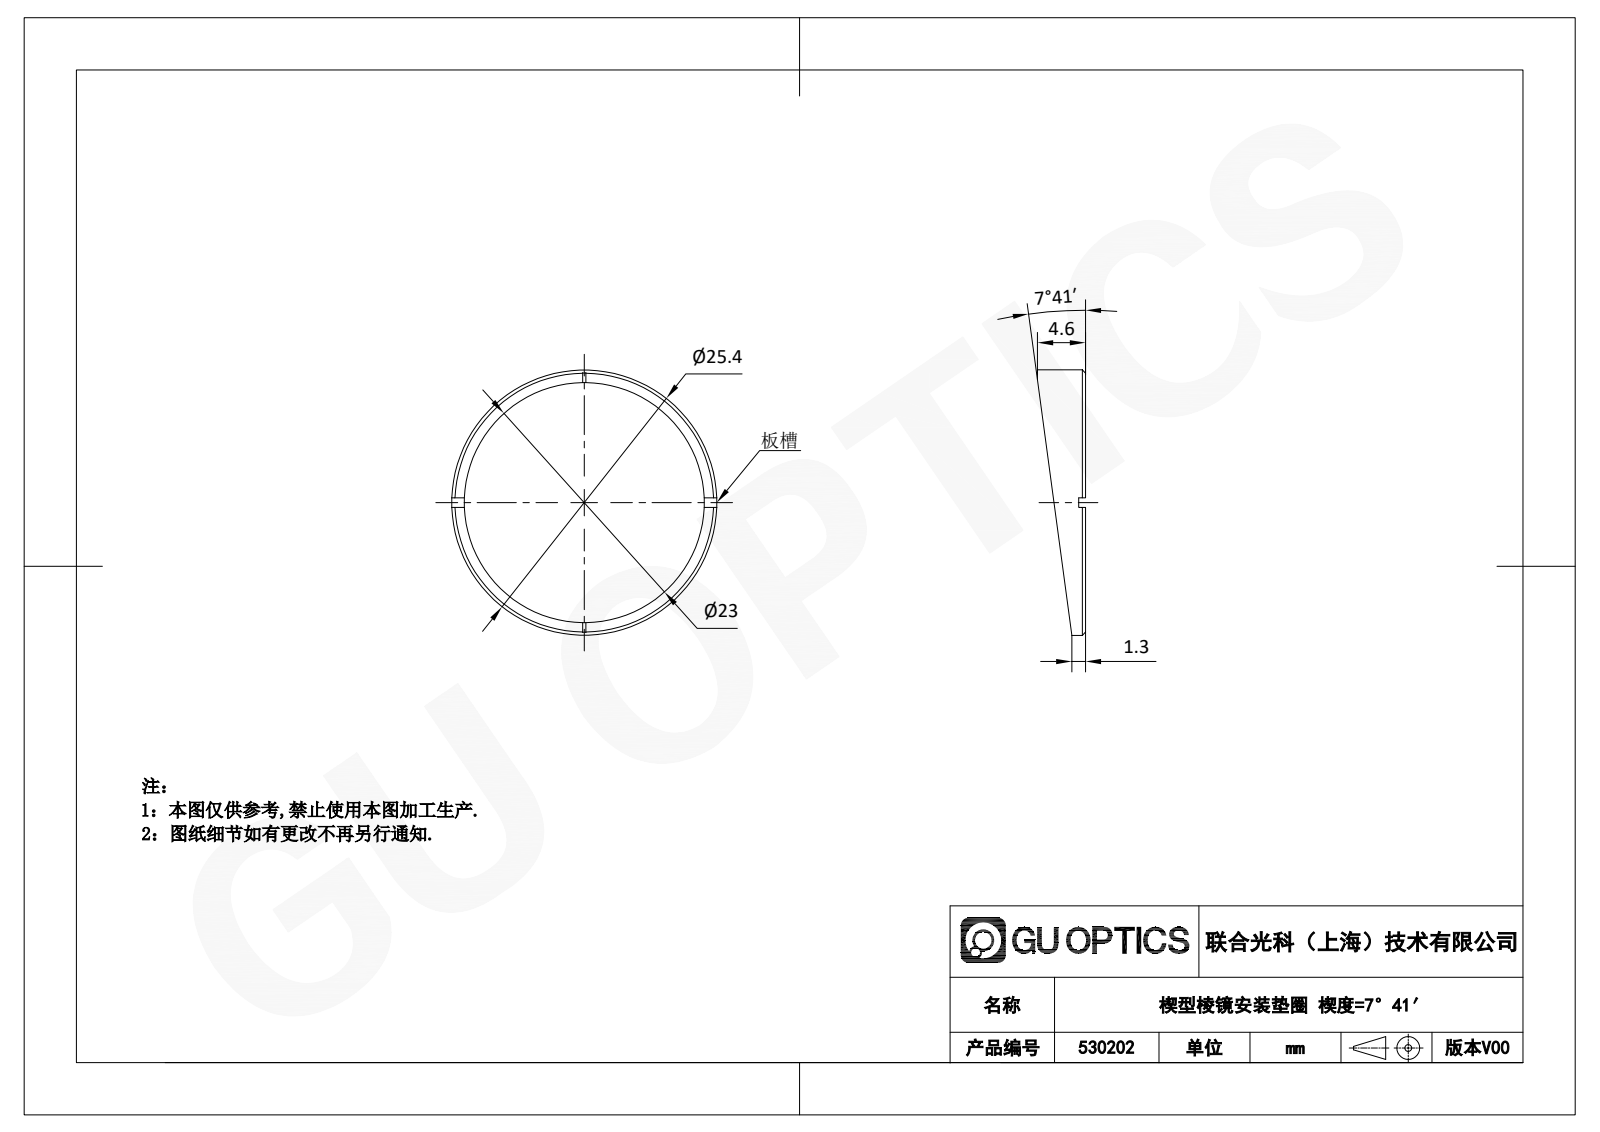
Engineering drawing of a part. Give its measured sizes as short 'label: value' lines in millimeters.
name: 530202
written by: SolidWorks 2020 (CONFIG_CONTROL_DESIGN)
unit: mm
bodies: 1 solid, 22 faces (18 planar, 2 cylindrical, 2 other)
size: 25.4 × 25.4 × 4.6
volume: 265 mm³; area: 622 mm²
holes: 1× ⌀23
bosses: 1× ⌀25.4
face distances: 4.6, 0.65, 3.95, 0.9, 0.64, 4.59
